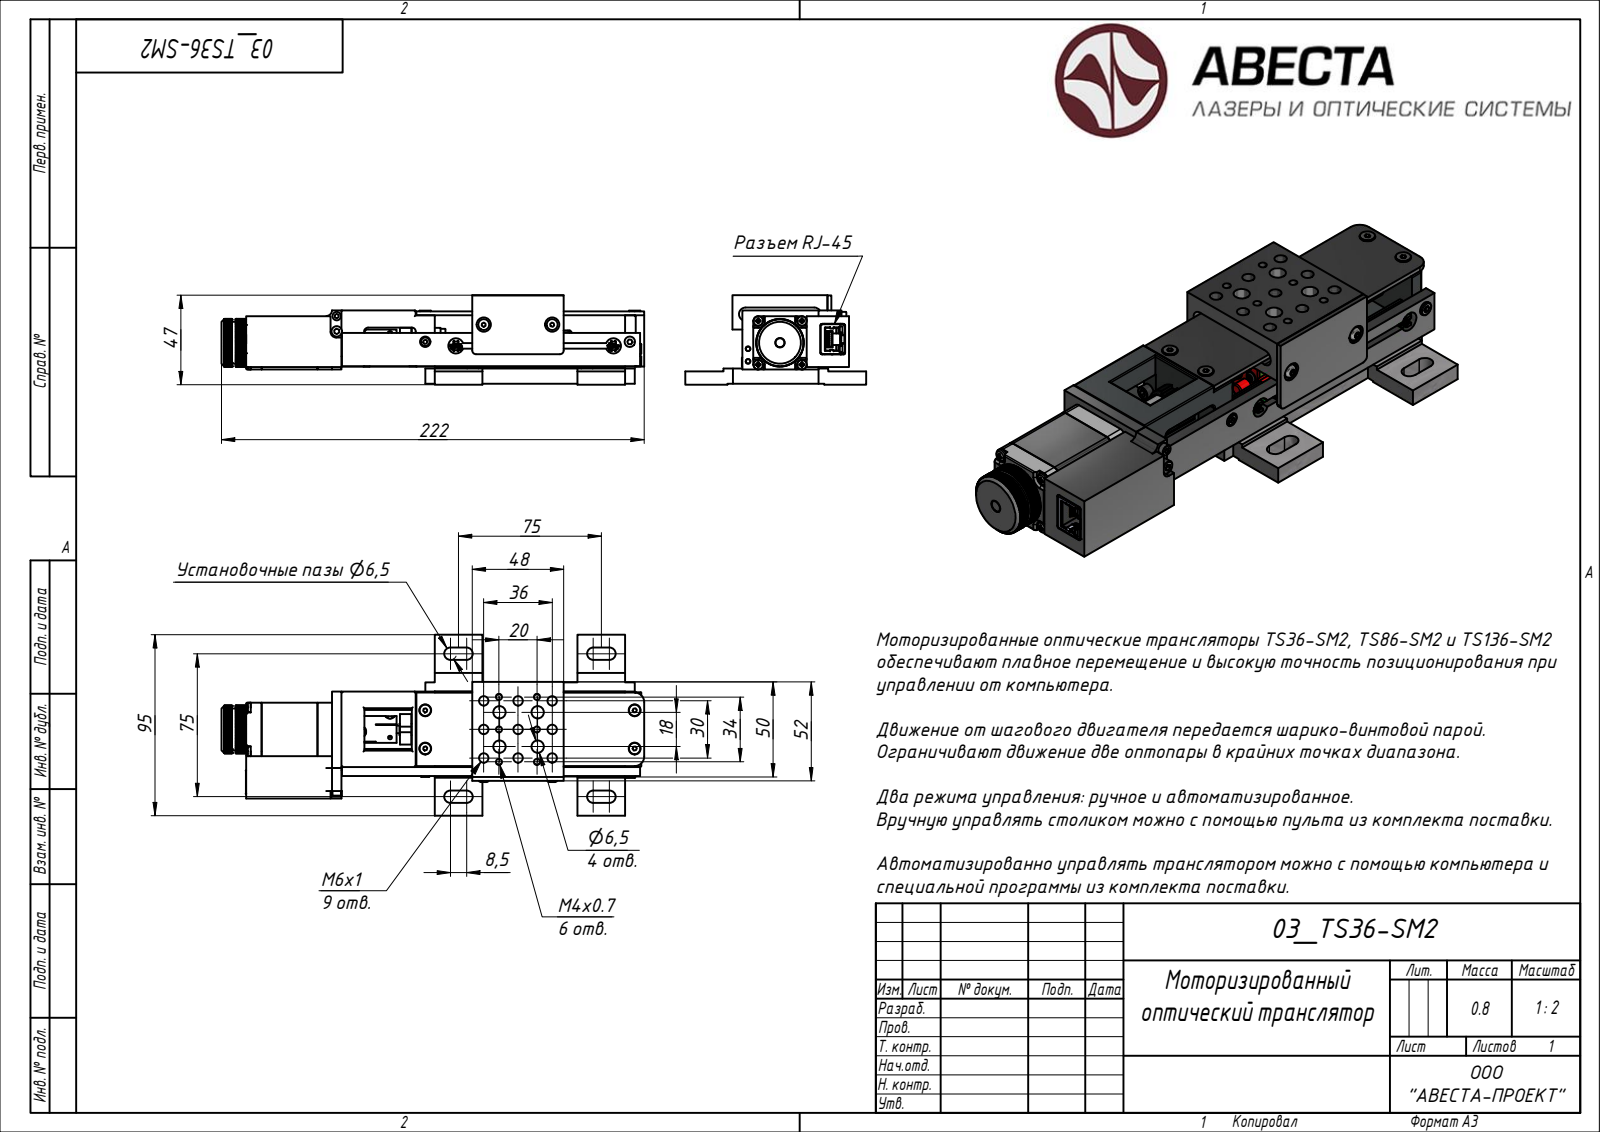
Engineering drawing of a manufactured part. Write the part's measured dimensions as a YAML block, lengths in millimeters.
step_written_by: "Rhino 7.34 (AUTOMOTIVE_DESIGN)"
units: millimeters
bodies: {solids: 1, faces: 2323, planar: 1434, cylindrical: 618, other: 271}
overall_size: [222, 95, 47]
volume: 248905
surface_area: 106634
round_holes:
  - {diameter: 3.4, count: 8}
  - {diameter: 6.5, count: 8}
  - {diameter: 2.46, count: 6}
  - {diameter: 3.24, count: 6}
  - {diameter: 4.92, count: 6}
  - {diameter: 1.05, count: 5}
  - {diameter: 2.5, count: 5}
  - {diameter: 3.8, count: 4}
  - {diameter: 5, count: 4}
  - {diameter: 2.15, count: 3}
  - {diameter: 7.5, count: 3}
  - {diameter: 2.01, count: 2}
round_bosses_or_shafts:
  - {diameter: 4.5, count: 10}
  - {diameter: 3, count: 7}
  - {diameter: 5.5, count: 6}
  - {diameter: 6, count: 5}
  - {diameter: 5.3, count: 4}
  - {diameter: 5, count: 3}
  - {diameter: 2.5, count: 3}
  - {diameter: 5.7, count: 2}
partial_cylinders:
  - {radius: 0.5, count: 36}
  - {radius: 2.5, count: 10}
  - {radius: 3, count: 10}
  - {radius: 2, count: 8}
  - {radius: 3.25, count: 8}
  - {radius: 1, count: 4}
  - {radius: 1.75, count: 2}
  - {radius: 2.4, count: 2}
face_to_face_distances: [0.5, 2, 8, 7, 2.5, 5.5, 5, 8.5, 38, 30]
hole_center_spacings: [18, 20, 9, 10, 17, 23.43, 26, 1]
